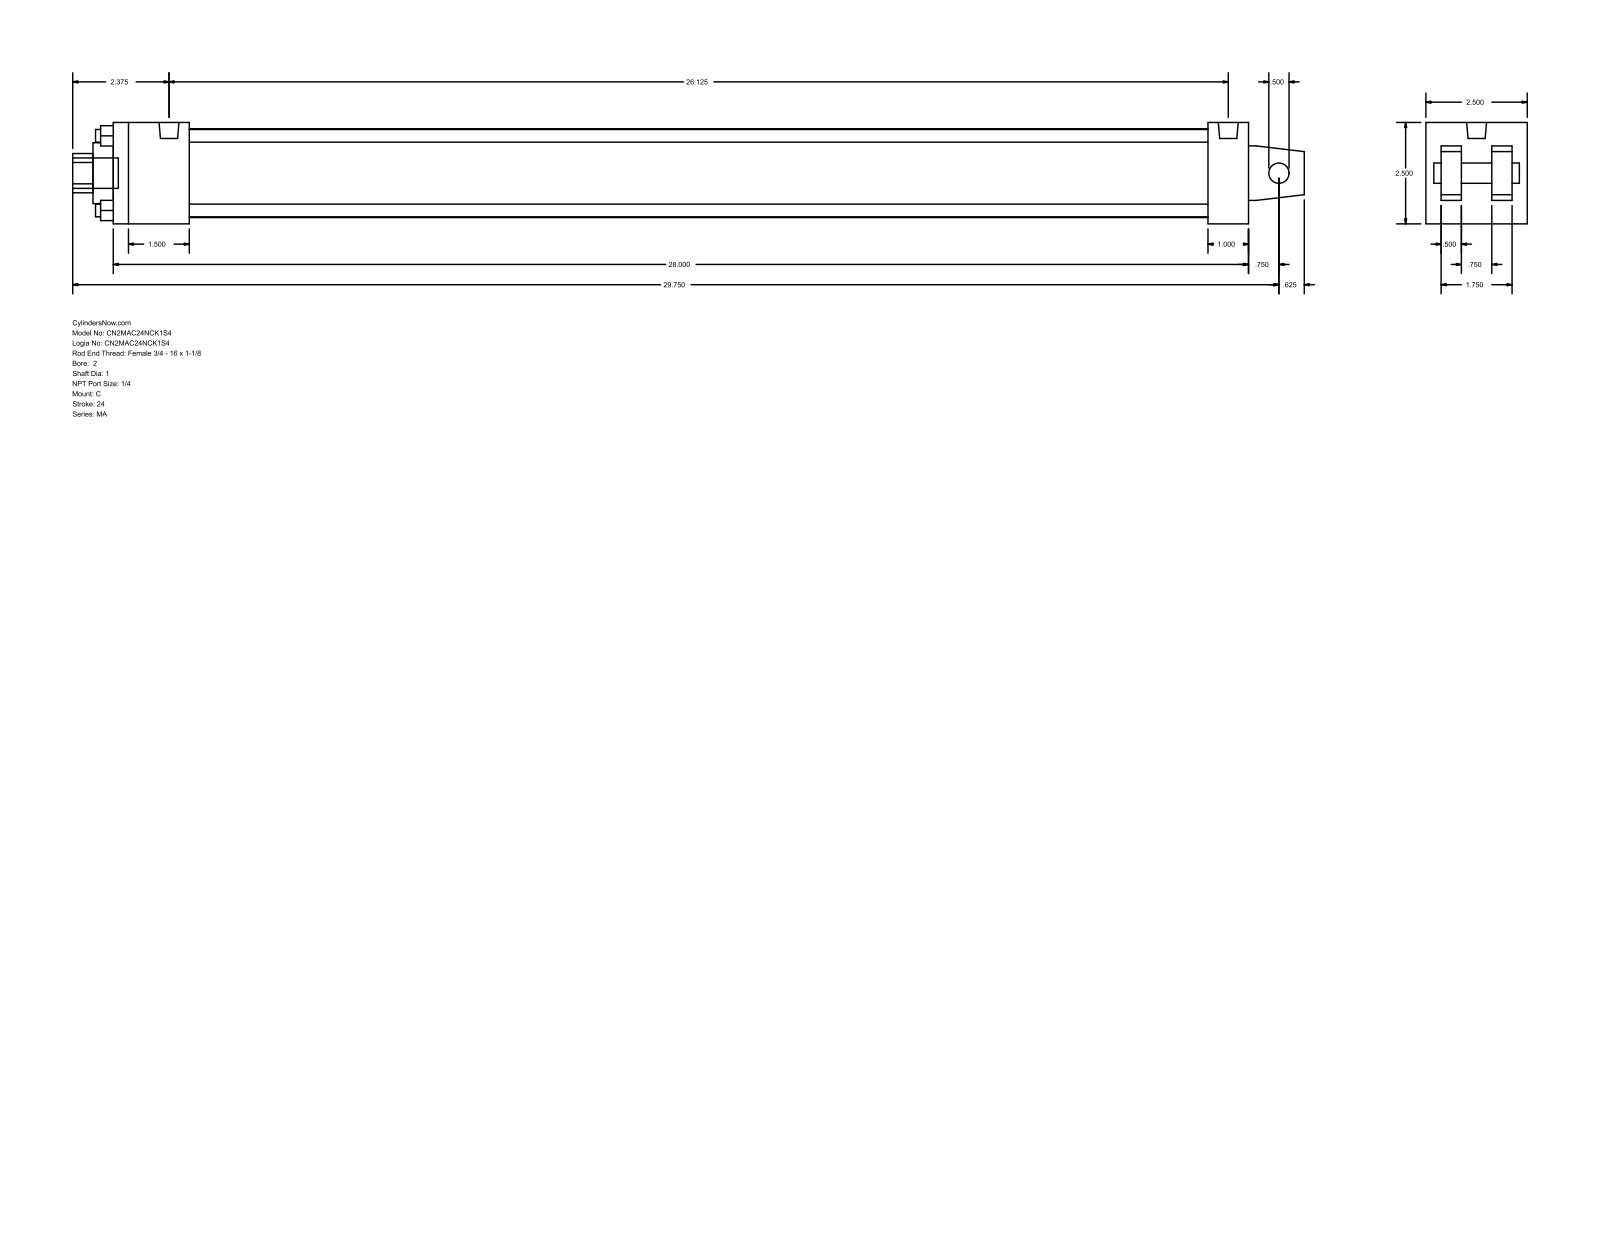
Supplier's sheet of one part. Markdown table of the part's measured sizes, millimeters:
| quantity | value |
| --- | --- |
| part name | MA_C__0200_1 |
| STEP written by | GSSL Pune (CONFIG_CONTROL_DESIGN) |
| units | millimeters |
| bodies | 0 solids, 103 faces (76 planar, 27 cylindrical, 0 other) |
| overall size | 771.52 × 63.5 × 63.5 |
| round holes (diameter × count) | 7.94 × 4, 12.7 × 1, 25.4 × 1, 38.1 × 1, 55.63 × 1 |
| round bosses / shafts (diameter × count) | 7.94 × 4, 12.49 × 2, 19.05 × 1 |
| partial cylindrical surfaces (radius × count) | 12.29 × 1 |
| main face-to-face distances | 63.5, 12.7, 711.2, 22.22, 41.28, 9.52, 53.98, 31.76, 47.63, 25.4 |
| hole center spacings | 33.05, 46.74, 66.1 |
